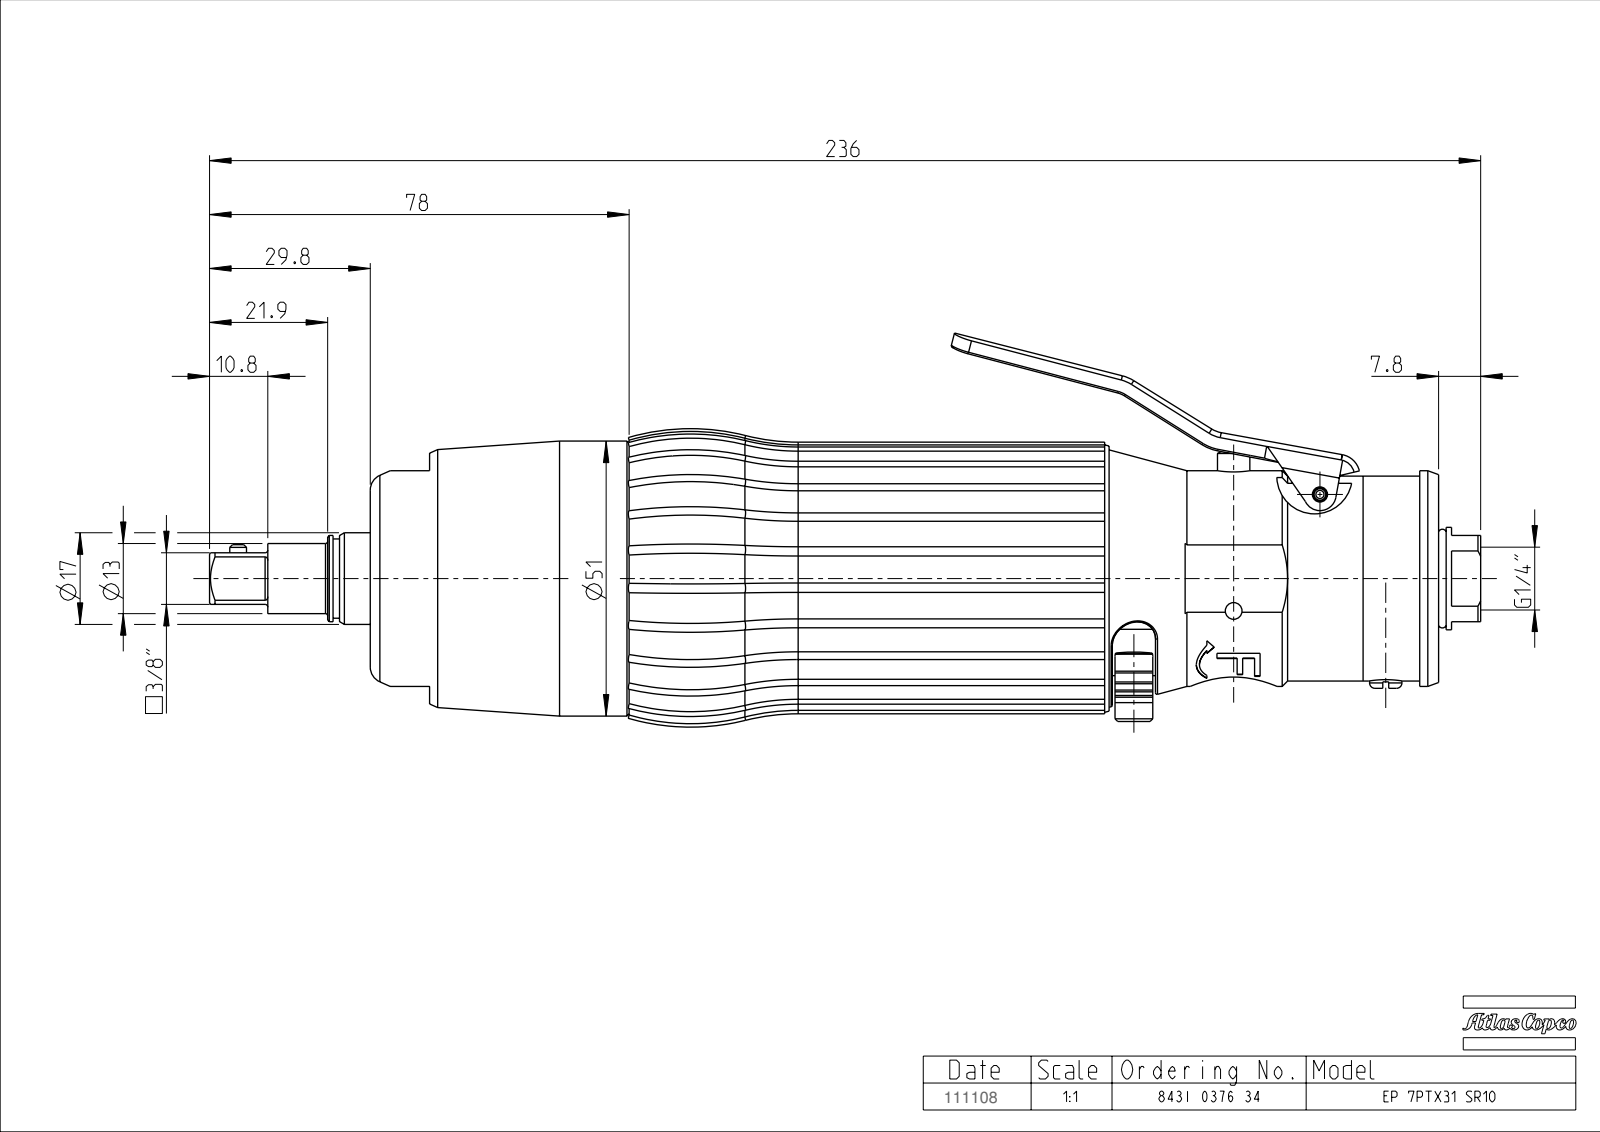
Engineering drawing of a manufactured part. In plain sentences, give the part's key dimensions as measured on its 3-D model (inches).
The part is named "EXT_COMP_SW0010". Its 3-D file was written by "CREO PARAMETRIC BY PTC INC, 2020281 (CONFIG_CONTROL_DESIGN)". It is 2 solids with 689 faces: 183 planar, 161 cylindrical and 345 other. Overall it measures 9.281 by 2.873 by 2.166 inches. Its volume is 21.39 cubic inches and its surface area 69.5 square inches. Round holes: 2 of diameter 0.122, 1 of diameter 0.059, 1 of diameter 0.079, 1 of diameter 0.11, 1 of diameter 0.185, 1 of diameter 0.213, 1 of diameter 0.248, 1 of diameter 0.459, 1 of diameter 0.472, 1 of diameter 0.512, 1 of diameter 0.61, 1 of diameter 1.441. Round bosses or shafts: 2 of diameter 0.236, 1 of diameter 2.008, 1 of diameter 1.575, 1 of diameter 1.496, 1 of diameter 1.437, 1 of diameter 0.748, 1 of diameter 0.669, 1 of diameter 0.63. Partial cylindrical surfaces (rounded edges, fillets, slot ends): 23 of radius 0.039, 8 of radius 0.012, 6 of radius 0.02, 4 of radius 0.138, 3 of radius 0.079, 2 of radius 0.069, 2 of radius 0.157, 1 of radius 0.118. The main face-to-face distances are 7.799, 0.039, 2.382, 5.417, 1.496, 0.126, 0.504, 0.472, 0.433, 0.098. The hole center spacings are 0.098, 1.058, 3.968, 4.631, 7.27.
